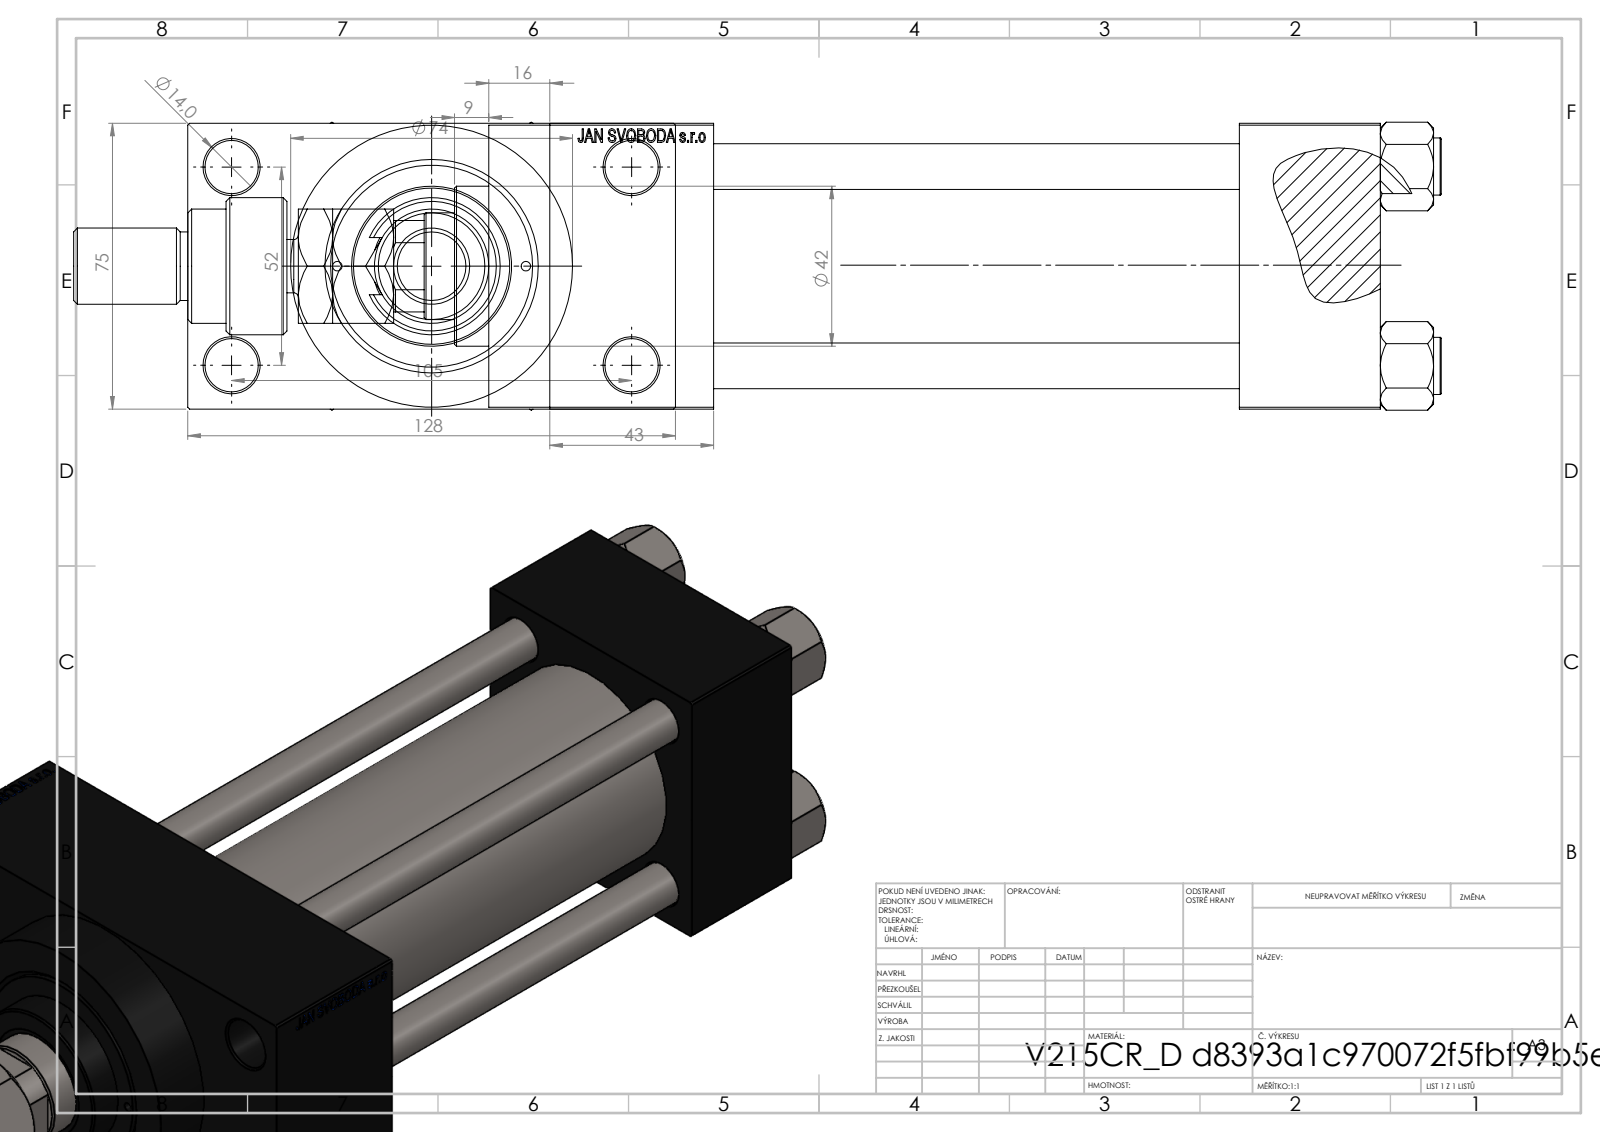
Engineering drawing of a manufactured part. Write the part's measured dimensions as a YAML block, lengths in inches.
part_name: "FEMALE_PART_FOR_DFA; V215CR_D_TYCINKA; V215CR_D_Body; V215_VC_A (+3 more)"
step_written_by: "SolidWorks 2019 (CONFIG_CONTROL_DESIGN)"
units: inches
bodies: {solids: 13, faces: 1196, planar: 527, cylindrical: 105, other: 564}
overall_size: [14.134, 5.039, 2.974]
volume: 59.82
surface_area: 355.8
round_holes:
  - {diameter: 0.472, count: 4}
  - {diameter: 0.551, count: 4}
  - {diameter: 0.098, count: 2}
  - {diameter: 0.276, count: 2}
  - {diameter: 0.825, count: 2}
  - {diameter: 1.181, count: 2}
  - {diameter: 0.728, count: 1}
  - {diameter: 1.102, count: 1}
  - {diameter: 1.22, count: 1}
  - {diameter: 1.614, count: 1}
  - {diameter: 1.969, count: 1}
  - {diameter: 2.087, count: 1}
round_bosses_or_shafts:
  - {diameter: 0.591, count: 4}
  - {diameter: 2.913, count: 1}
  - {diameter: 2.205, count: 1}
  - {diameter: 1.654, count: 1}
  - {diameter: 1.417, count: 1}
  - {diameter: 1.181, count: 1}
  - {diameter: 0.866, count: 1}
  - {diameter: 0.787, count: 1}
partial_cylinders:
  - {radius: 0.295, count: 1}
  - {radius: 0.472, count: 1}
  - {radius: 0.531, count: 1}
face_to_face_distances: [2.953, 5.433, 1.457, 6.89, 1.043, 1.693, 8.583, 7.126, 3.996, 0.63]
hole_center_spacings: [1.031, 1.037, 1.456, 1.497, 2.059, 2.253, 2.3, 2.307]
